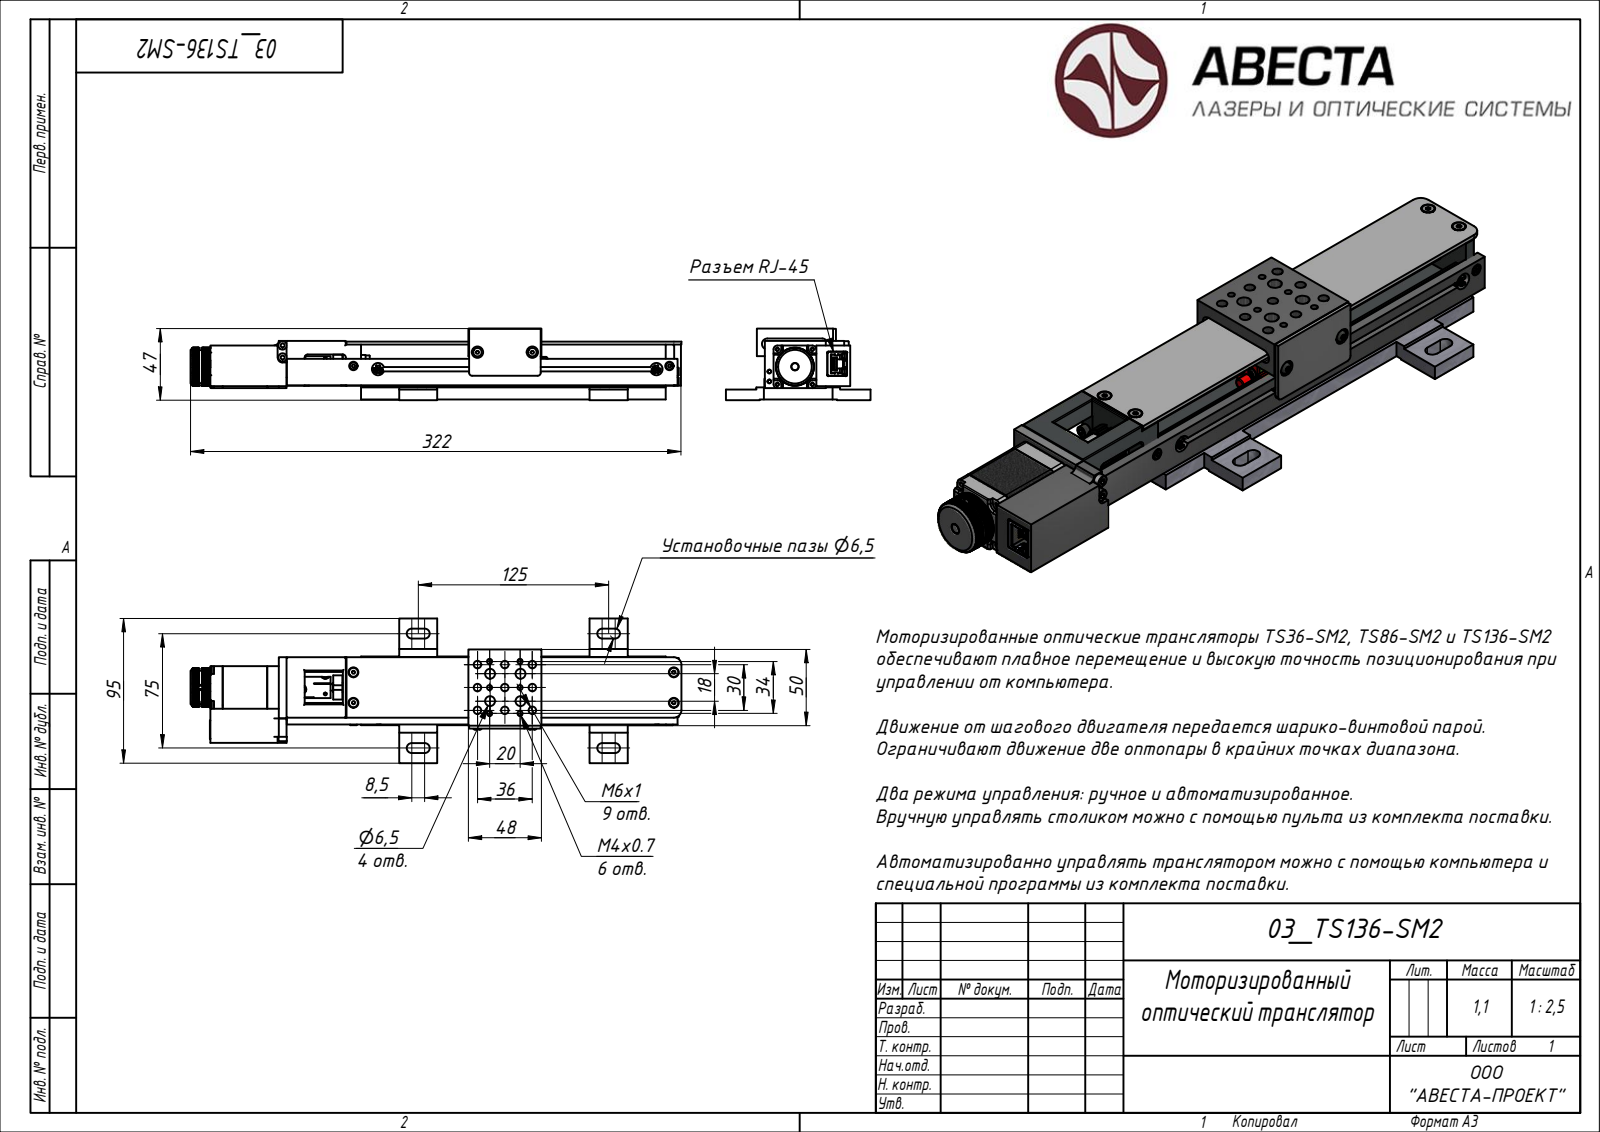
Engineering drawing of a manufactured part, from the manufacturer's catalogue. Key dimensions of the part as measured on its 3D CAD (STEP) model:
STEP written by: Rhino 7.34 (AUTOMOTIVE_DESIGN)
Units: millimetres
Bodies: 1 solid, 2229 faces (1387 planar, 651 cylindrical, 191 other)
Overall size (bounding box): 322.3 × 95 × 47
Volume: 327 869 mm³ · Surface area: 143 081 mm²
Round holes (diameter × count): ⌀6.5 ×14, ⌀3.4 ×10, ⌀2.5 ×7, ⌀4.92 ×7, ⌀3.24 ×6, ⌀1.05 ×5, ⌀2.46 ×5, ⌀2.2 ×4, ⌀3.8 ×4, ⌀5 ×4, ⌀2.15 ×3, ⌀2.46 ×3
Round bosses / shafts (diameter × count): ⌀4.5 ×10, ⌀5.5 ×6, ⌀3 ×6, ⌀6 ×5, ⌀5.3 ×4, ⌀2.5 ×4, ⌀5 ×3, ⌀5.7 ×2
Partial cylindrical surfaces — rounded edges, fillets, slot ends (radius × count): R0.5 ×36, R2.5 ×10, R3 ×10, R2 ×8, R3.25 ×8, R1 ×4, R1.75 ×2, R2.4 ×2
Main face-to-face distances: 0.5, 2, 8, 38, 28, 36, 30, 8.5, 5.5, 29.5
Hole centre spacings: 18, 20, 17, 23.43, 15, 1, 8.01, 8.25
